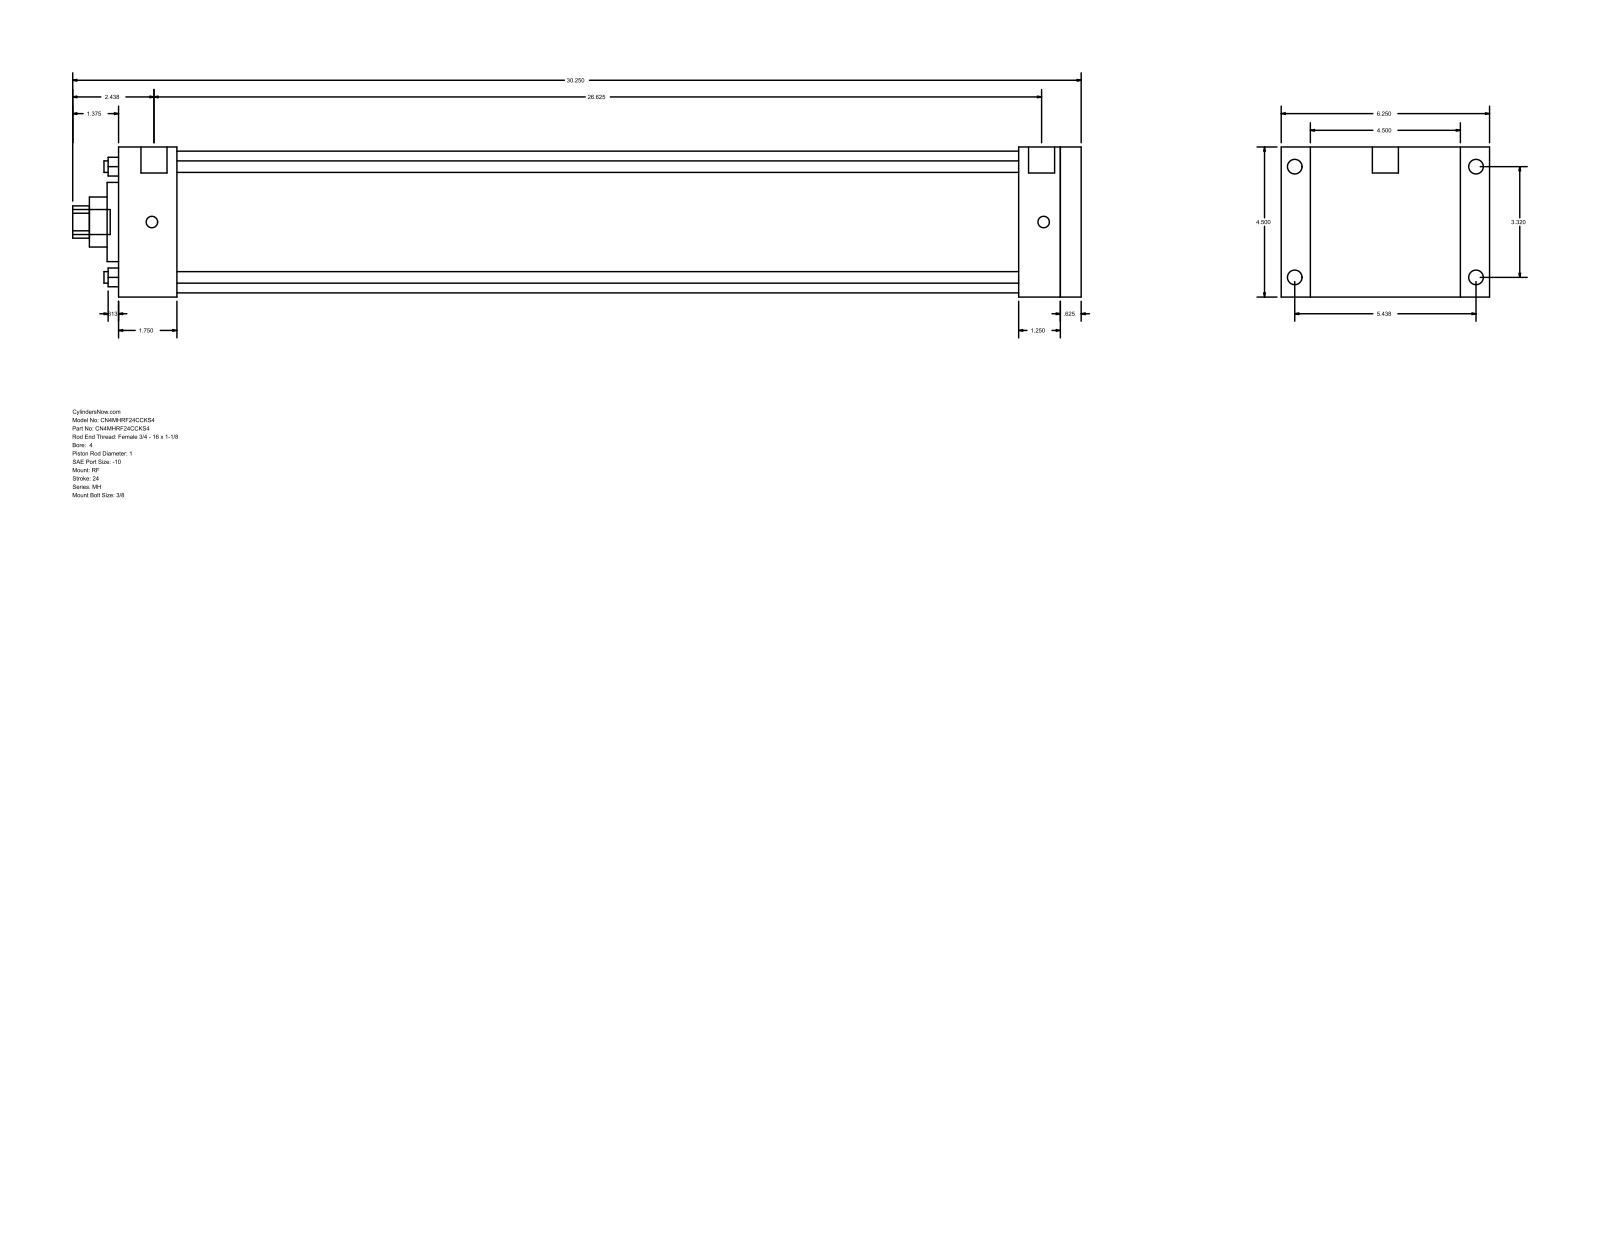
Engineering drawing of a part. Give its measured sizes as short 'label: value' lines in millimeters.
name: MH_RF__0400_1
written by: GSSL Pune (CONFIG_CONTROL_DESIGN)
unit: mm
bodies: 0 solids, 94 faces (65 planar, 29 cylindrical, 0 other)
size: 768.35 × 158.75 × 114.3
holes: 4× ⌀8.76, 1× ⌀25.4, 1× ⌀38.1, 1× ⌀60.33, 1× ⌀107.95
bosses: 4× ⌀11.13, 4× ⌀8.73, 2× ⌀19.84, 1× ⌀19.05
rounds: 1× R12.29
face distances: 114.3, 733.43, 15.87, 717.56, 44.46, 673.1, 688.97, 685.81, 641.35, 31.75
hole spacings: 59.62, 84.32, 119.25
